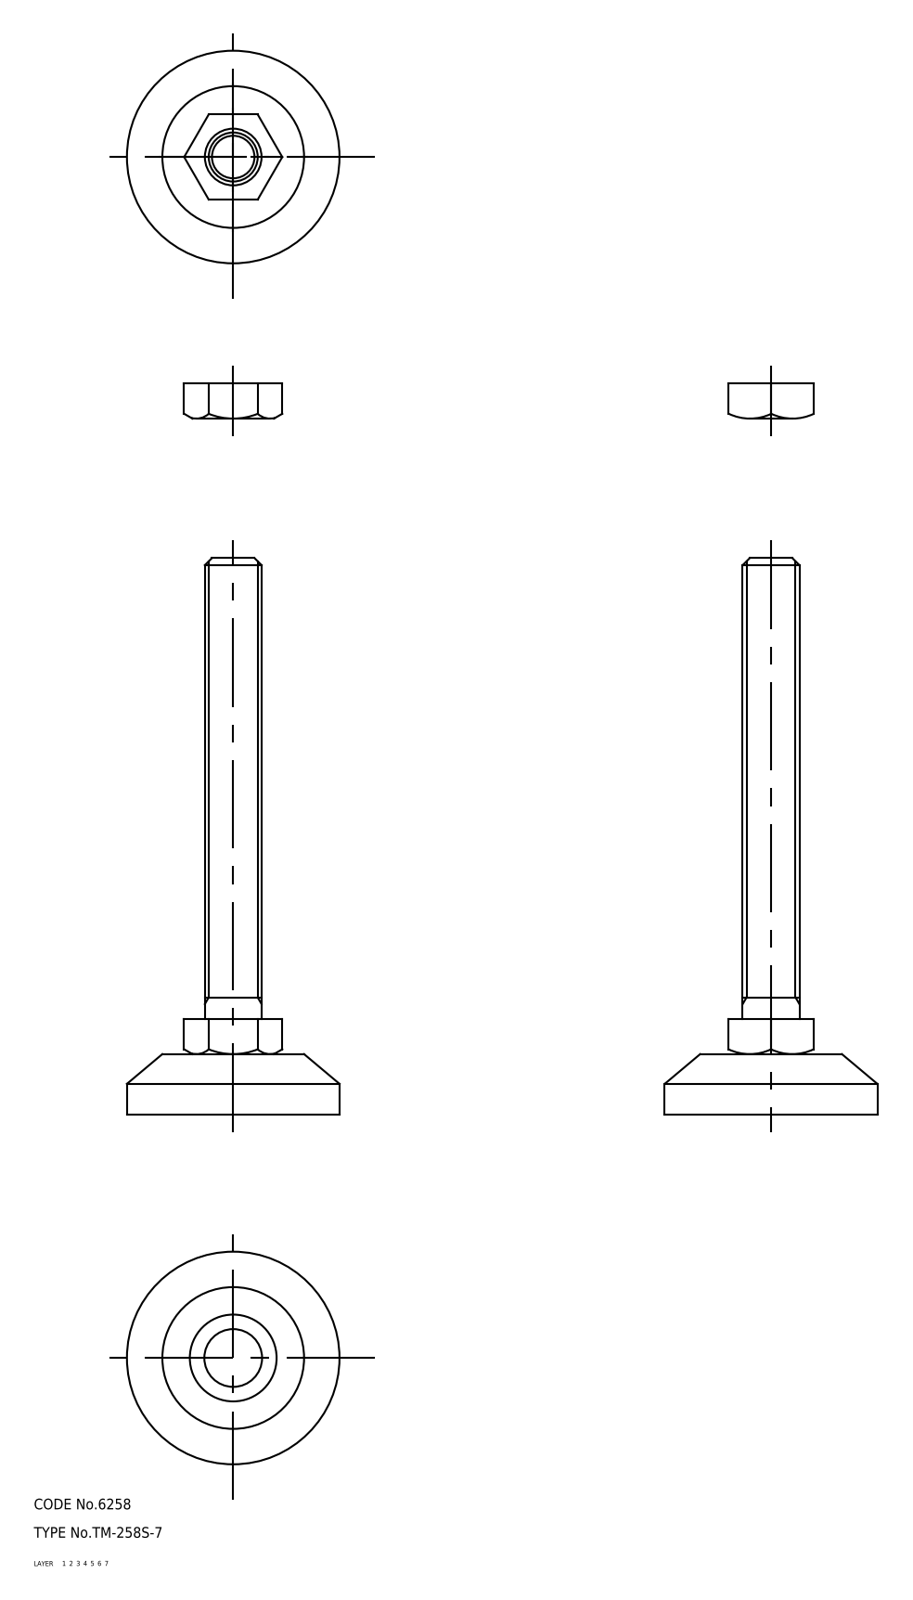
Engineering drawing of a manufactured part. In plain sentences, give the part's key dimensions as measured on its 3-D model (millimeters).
The part is named "67112353; 67112366; 67112379". Its 3-D file was written by "CADfix (AUTOMOTIVE_DESIGN)". It is 3 solids with 67 faces: 0 planar, 0 cylindrical and 67 other. Overall it measures 157 by 60 by 60 millimeters. Its volume is 66 150 cubic millimeters and its surface area 19 590 square millimeters.
